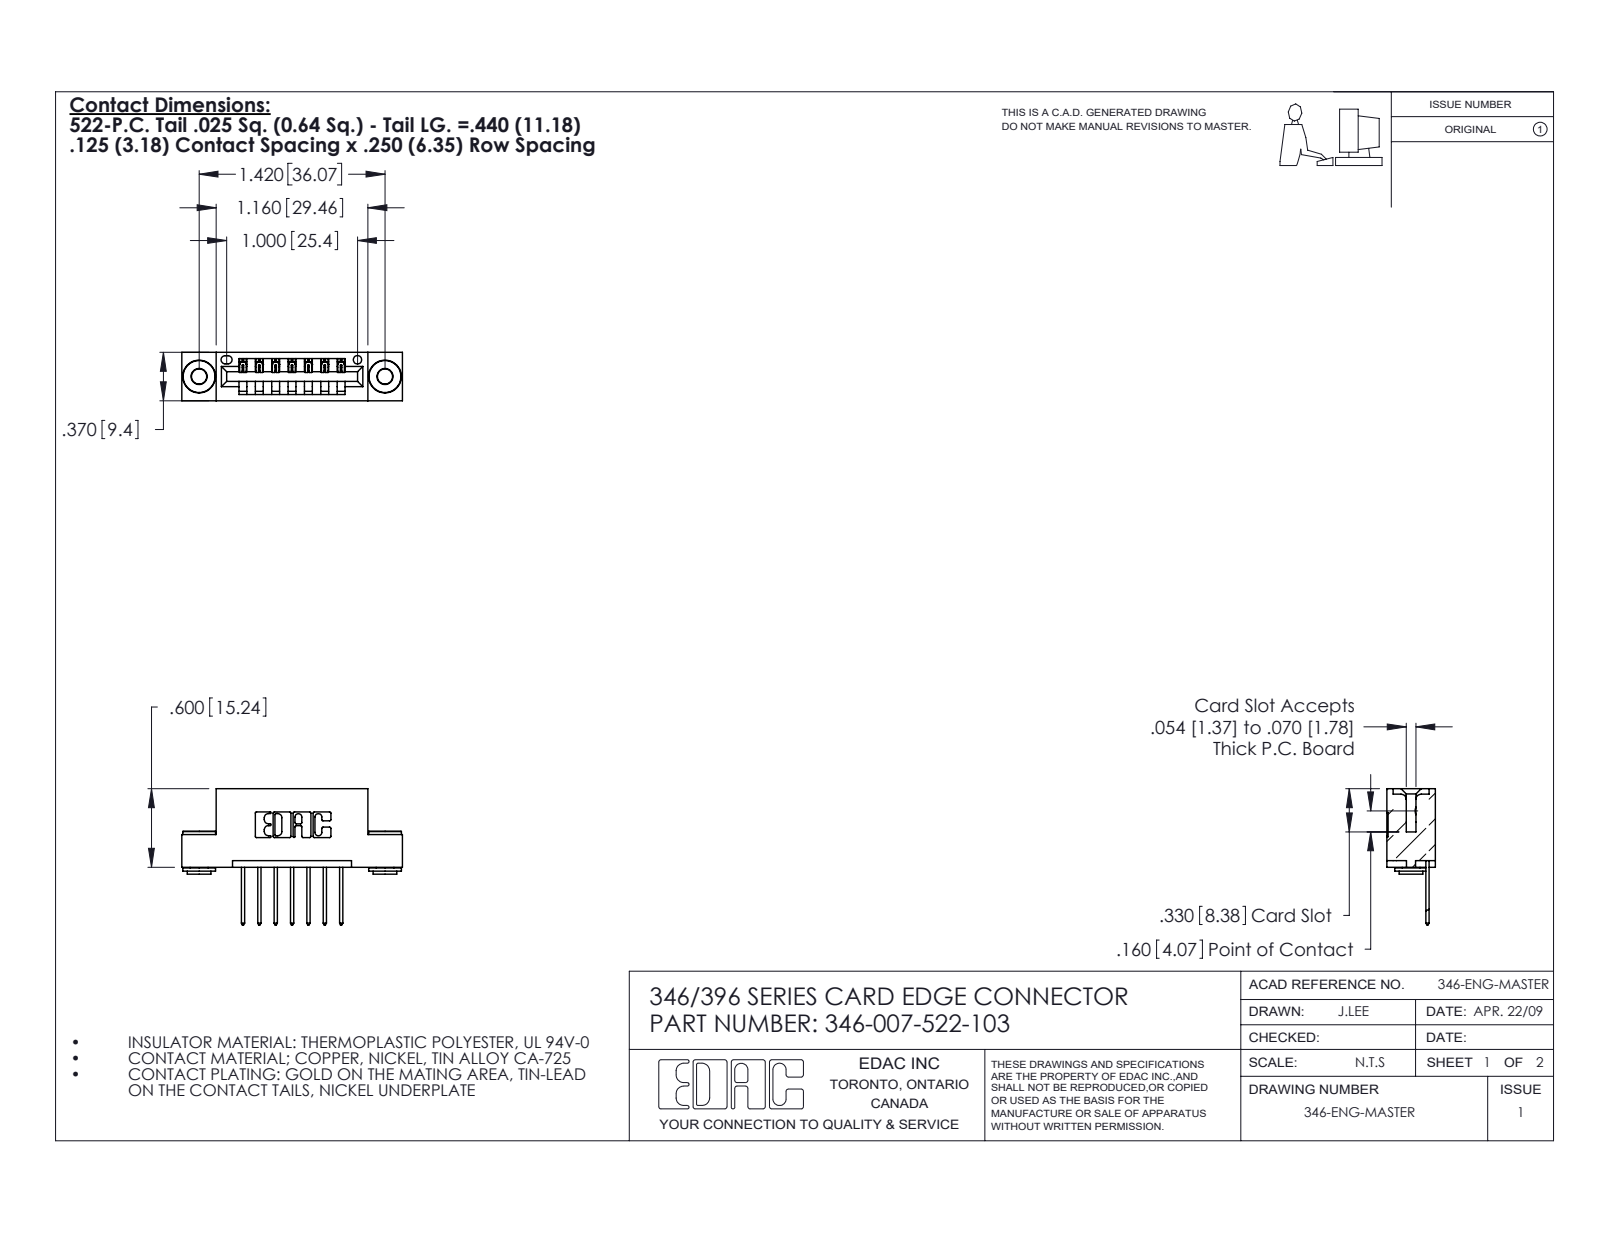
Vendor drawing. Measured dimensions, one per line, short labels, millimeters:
name: 345-292-001_345-293-122; 346 Part_Flush Mounting Lugs - 0.156 Dia-TH; 346-007-522-103; 345-250-002_345-250-002-102
written by: SolidWorks 2020 (CONFIG_CONTROL_DESIGN)
unit: mm
bodies: 10 solids, 580 faces (380 planar, 192 cylindrical, 8 other)
size: 42.8 × 26.4 × 9.4
volume: 3 850 mm³; area: 4 721 mm²
holes: 2× ⌀2.9, 2× ⌀4, 1× ⌀1.6
bosses: 2× ⌀6.4, 2× ⌀4.6, 2× ⌀3.5
rounds: 22× R0.3, 14× R0.2, 14× R0.3, 6× R0.2, 6× R0.8, 3× R0.7, 2× R0.8, 2× R1
face distances: 6.4, 9.4, 1.2, 8.2, 0.6, 1.8, 7.6, 3.8, 5.6, 2.5
hole spacings: 6.2, 30.9, 36.1
